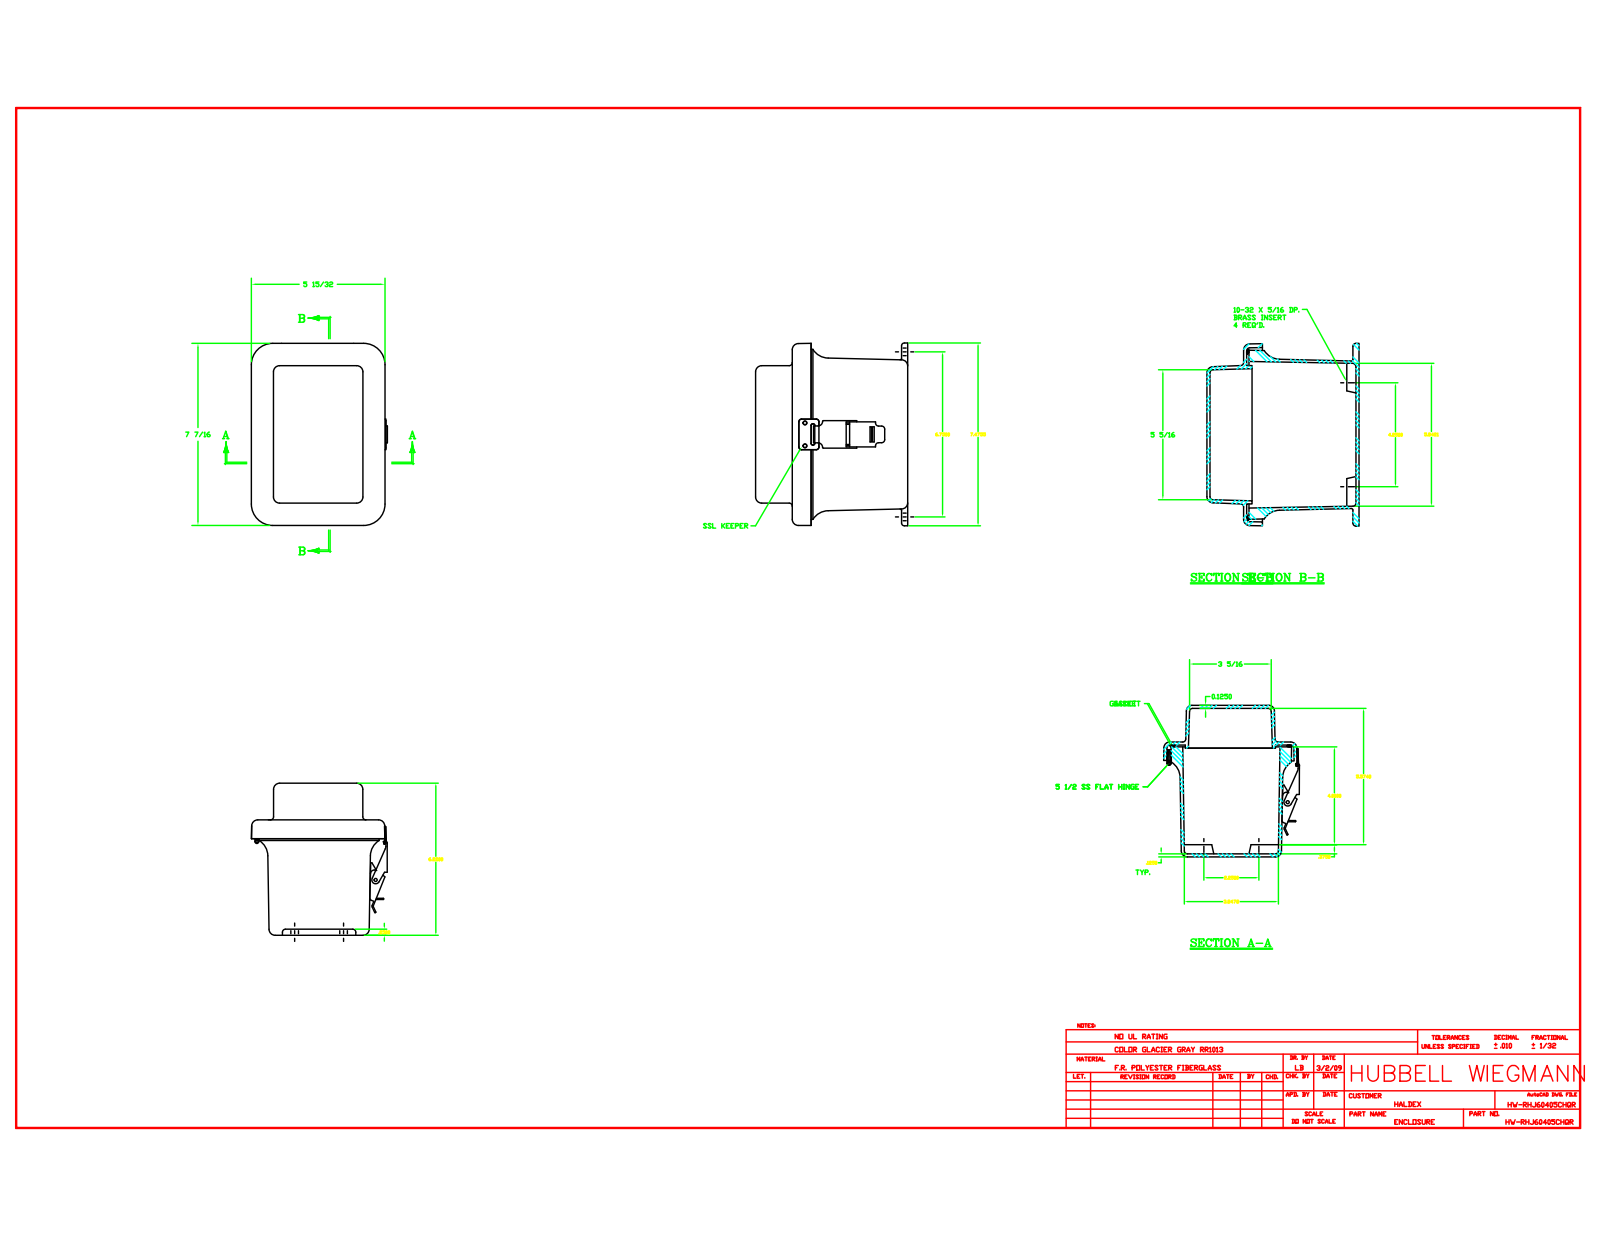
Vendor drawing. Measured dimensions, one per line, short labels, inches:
name: J604HL_6; RMINS45821P_63; RMINS45821P_64; RMINS45821P_65 (+8 more)
written by: Autodesk Inventor 2014 (AUTOMOTIVE_DESIGN)
unit: in
bodies: 25 solids, 694 faces (272 planar, 274 cylindrical, 148 other)
size: 7.474 × 6.227 × 5.601
volume: 33.68 in³; area: 460.9 in²
holes: 11× ⌀0.14, 5× ⌀0.131, 5× ⌀0.152, 4× ⌀0.104, 4× ⌀0.156, 4× ⌀0.218, 2× ⌀0.13, 2× ⌀0.135, 1× ⌀0.085, 1× ⌀0.375
bosses: 9× ⌀0.125, 5× ⌀0.25, 4× ⌀0.27, 1× ⌀0.3, 1× ⌀0.17, 1× ⌀0.155, 1× ⌀0.12
rounds: 24× R0.125, 20× R0.031, 12× R0.015, 12× R0.25, 8× R0.045, 6× R0.03, 5× R0.022, 4× R0.06
face distances: 0.125, 4.602, 6.102, 1.5, 6.227, 1.625, 4.477, 5.977, 0.774, 4.727
hole spacings: 0.937, 2.5, 3.339, 0.75, 0.469, 0.5, 1.341, 1.467
